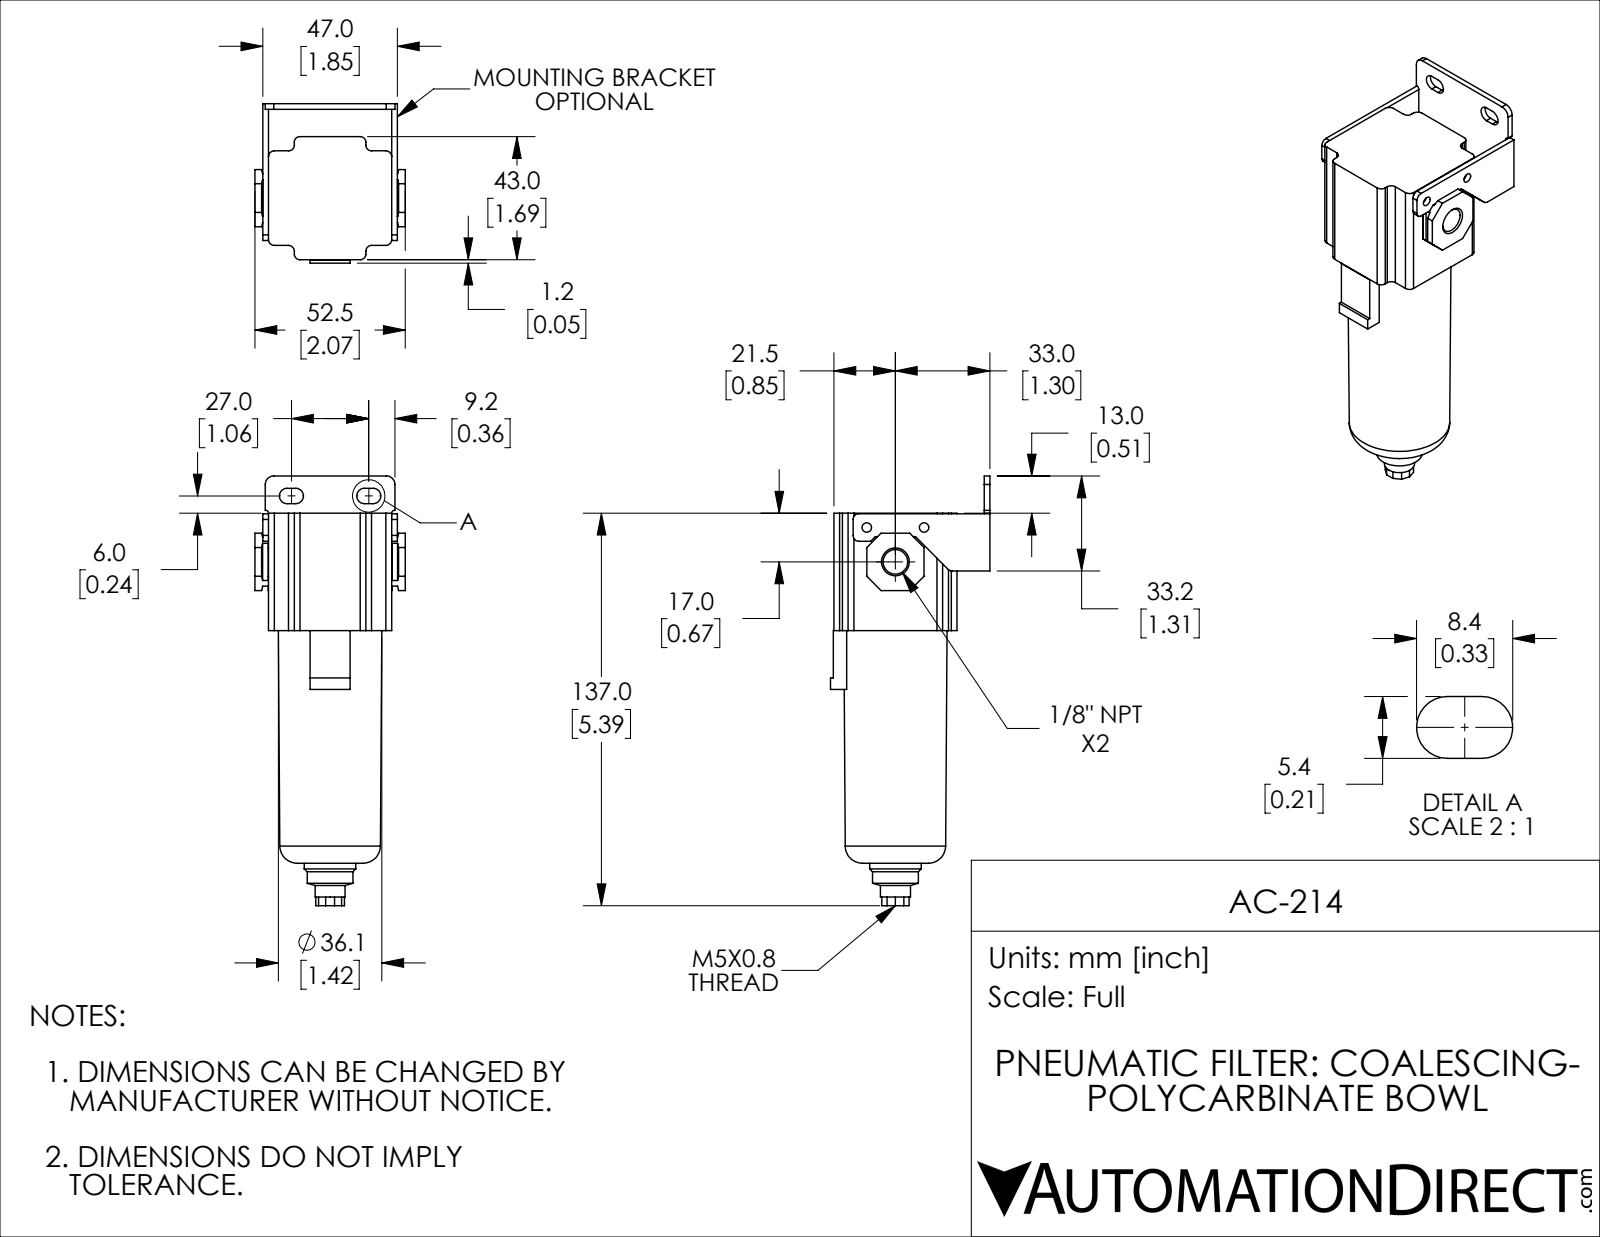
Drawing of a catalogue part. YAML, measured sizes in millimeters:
part_name: "AC-214"
step_written_by: "SolidWorks 2018 (AUTOMOTIVE_DESIGN)"
units: millimeters
bodies: {solids: 1, faces: 187, planar: 125, cylindrical: 48, other: 14}
overall_size: [150, 55.7, 52.5]
volume: 158500
surface_area: 26050
round_holes:
  - {diameter: 3.3, count: 2}
  - {diameter: 4.1, count: 1}
  - {diameter: 8.6, count: 1}
round_bosses_or_shafts:
  - {diameter: 18, count: 1}
  - {diameter: 16, count: 1}
  - {diameter: 10.5, count: 1}
partial_cylinders:
  - {radius: 2, count: 15}
  - {radius: 2.7, count: 4}
  - {radius: 1, count: 2}
  - {radius: 3, count: 2}
face_to_face_distances: [2, 43, 45, 52.5, 11.5, 54.5, 9.5, 5, 38, 41]
hole_center_spacings: [15.6, 20]
